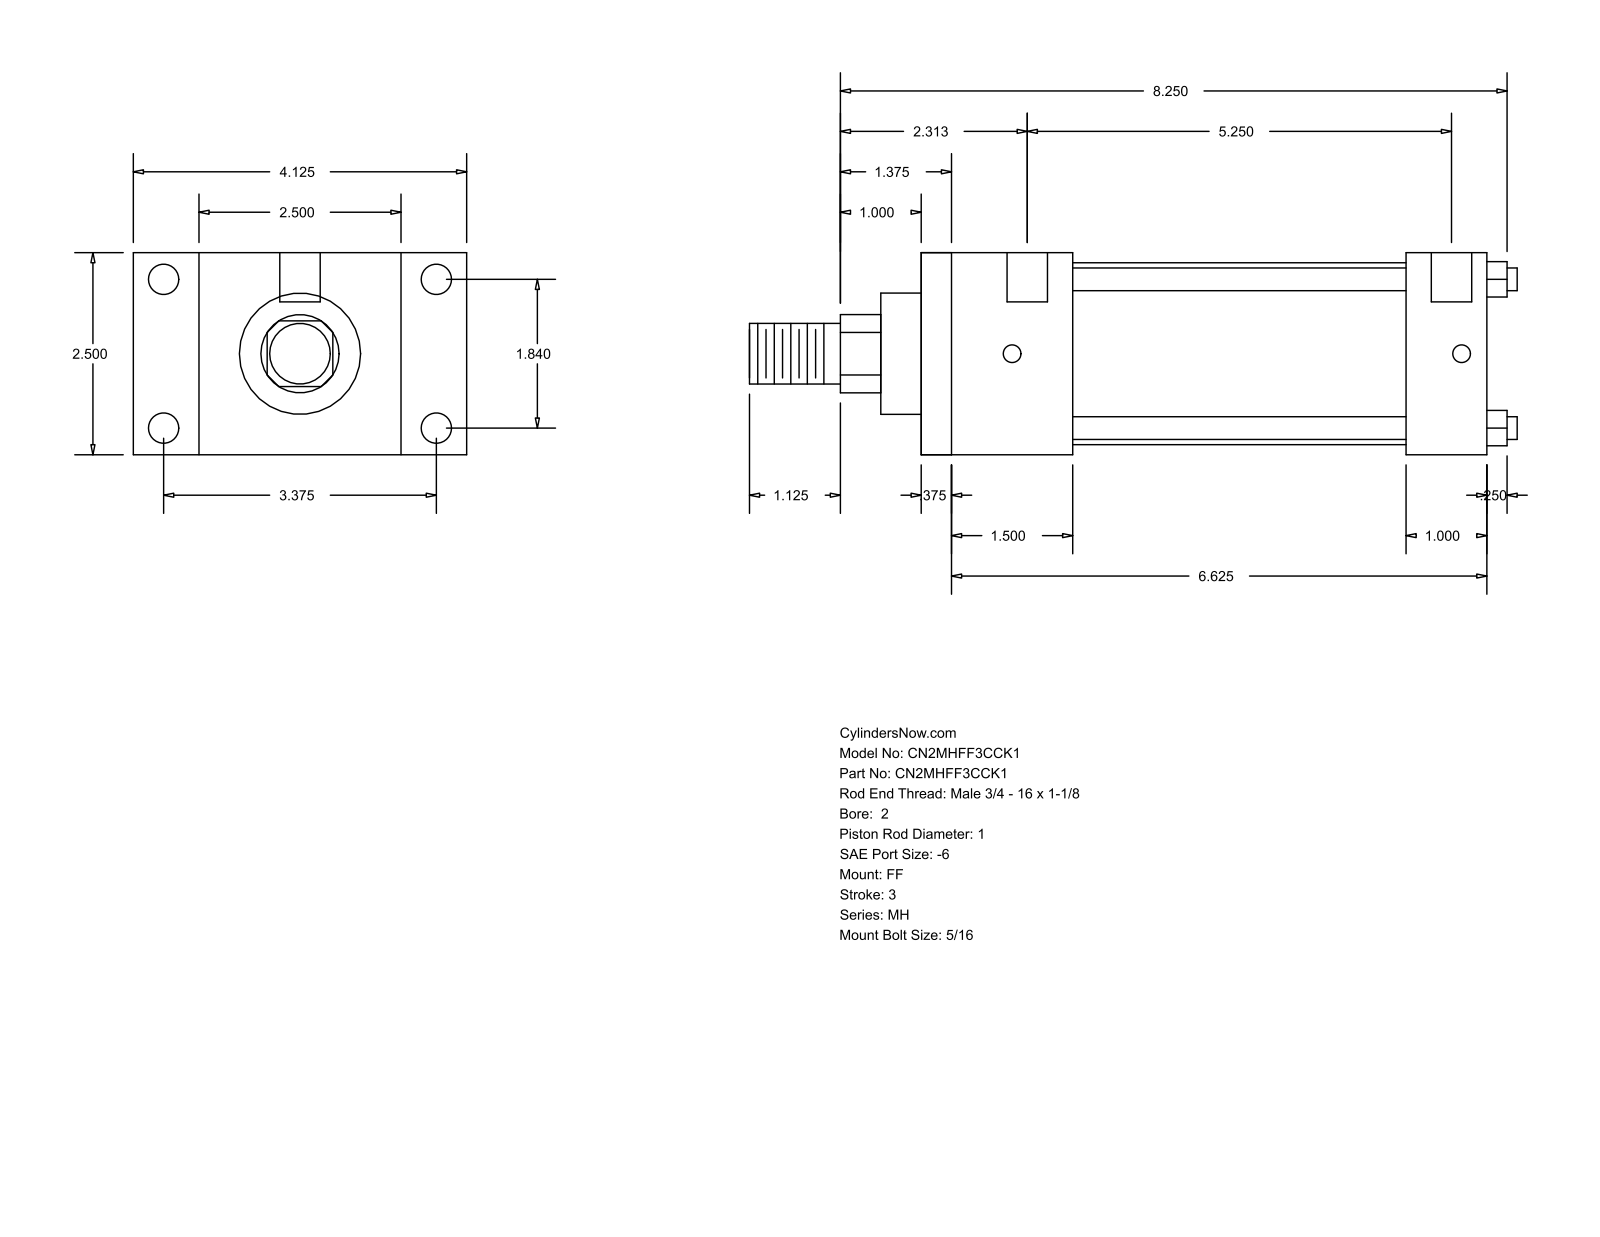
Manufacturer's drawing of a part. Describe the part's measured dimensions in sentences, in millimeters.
The part is named "MH_FF__0200_1". Its 3-D file was written by "GSSL Pune (CONFIG_CONTROL_DESIGN)". It is 0 solids with 92 faces: 64 planar, 28 cylindrical and 0 other. Overall it measures 241.3 by 104.78 by 63.5 millimeters. Round holes: 4 of diameter 5.56, 4 of diameter 9.53, 2 of diameter 12.7. Round bosses or shafts: 4 of diameter 7.14, 1 of diameter 57.15, 1 of diameter 38.1, 1 of diameter 25.4, 1 of diameter 19.05. Partial cylindrical surfaces (rounded edges, fillets, slot ends): 1 of radius 12.29. The main face-to-face distances are 63.5, 177.8, 9.52, 168.28, 20.64, 25.4, 47.63, 152.4, 38.11, 142.88. The hole center spacings are 46.74, 85.72, 97.63, 141.28, 3.17, 4.76, 133.35, 136.52.
